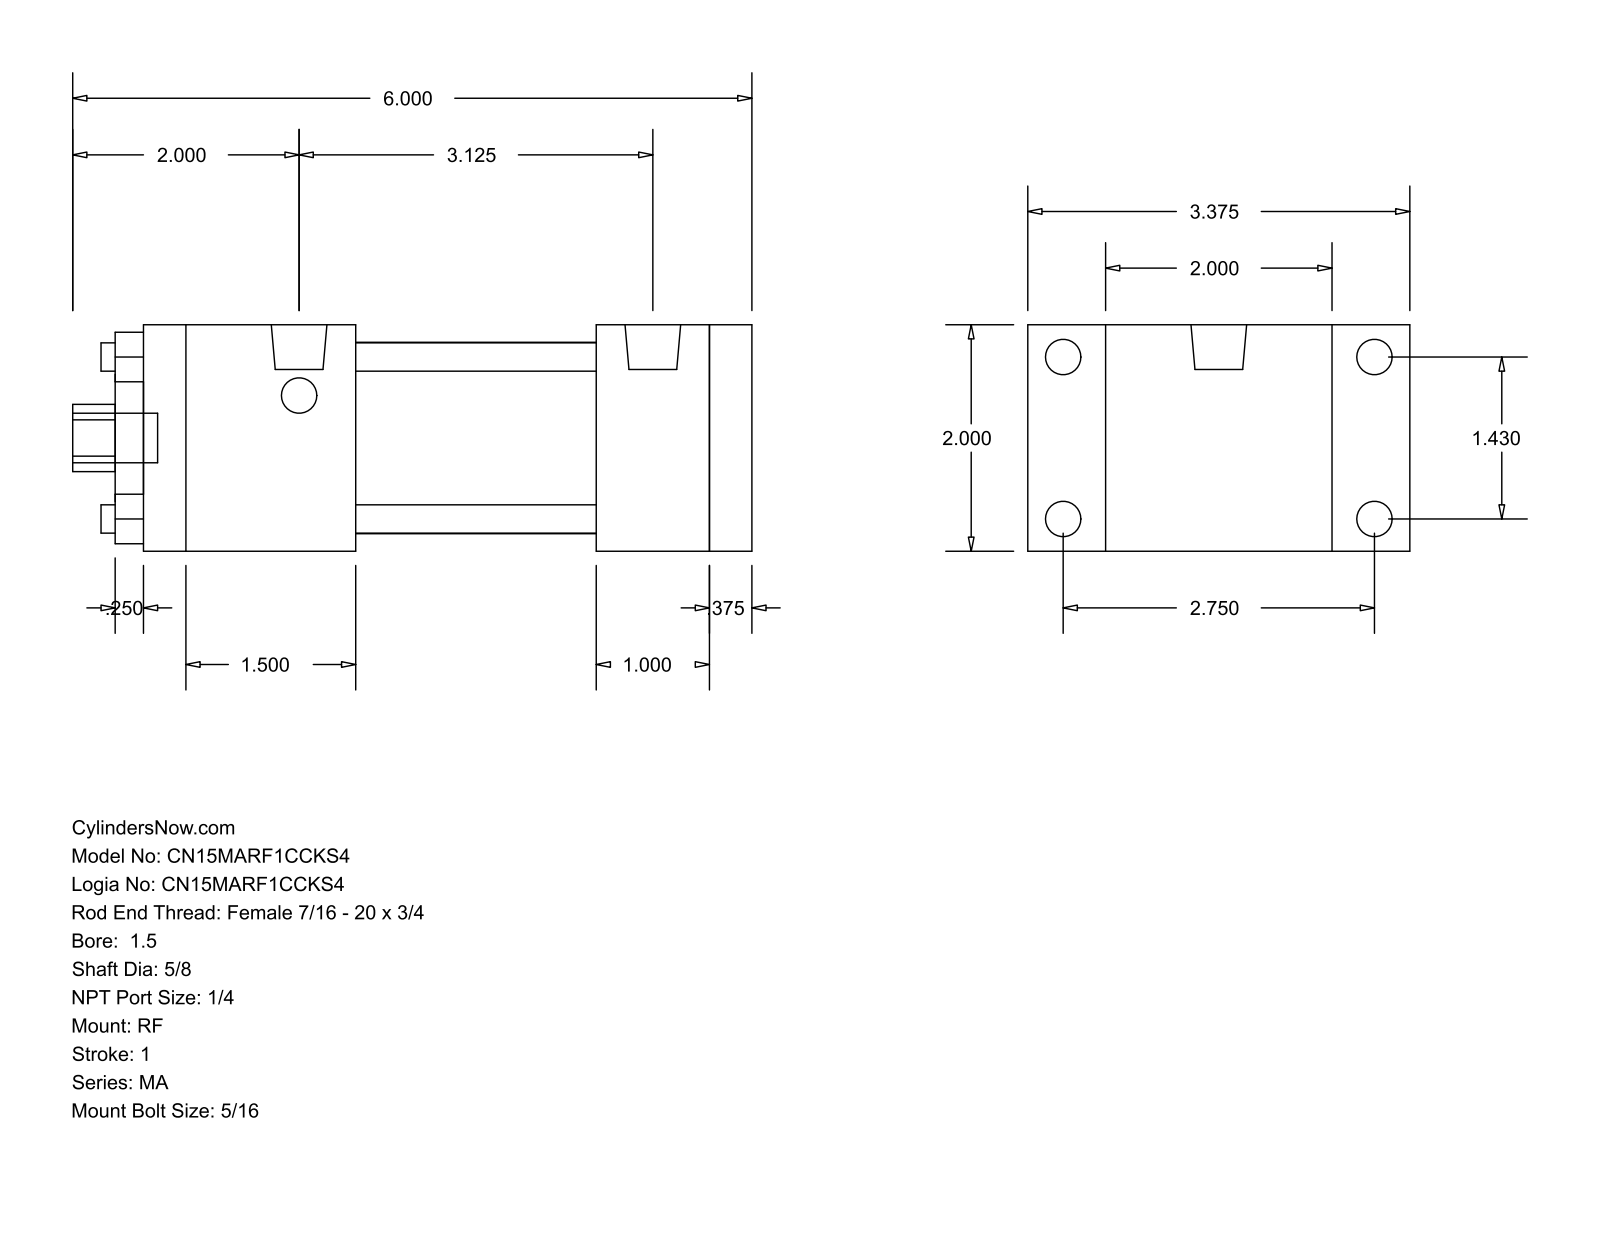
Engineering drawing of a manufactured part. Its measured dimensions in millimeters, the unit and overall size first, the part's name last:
Units: millimetres
Overall size (bounding box): 152.4 × 85.72 × 50.8
Round holes (diameter × count): ⌀6.35 ×4, ⌀15.88 ×1, ⌀28.57 ×1, ⌀42.93 ×1
Round bosses / shafts (diameter × count): ⌀7.94 ×8, ⌀12.49 ×2, ⌀11.11 ×1
Partial cylindrical surfaces — rounded edges, fillets, slot ends (radius × count): R7.54 ×1
Main face-to-face distances: 50.8, 53.97, 9.52, 127, 136.52, 101.59, 25.41, 34.93, 47.62, 79.38
Hole centre spacings: 25.68, 36.32, 51.36
Bodies: 0 solids, 92 faces (64 planar, 28 cylindrical, 0 other)
Part name (STEP PRODUCT): MA_RF__0150_0.625
STEP written by: GSSL Pune (CONFIG_CONTROL_DESIGN)
